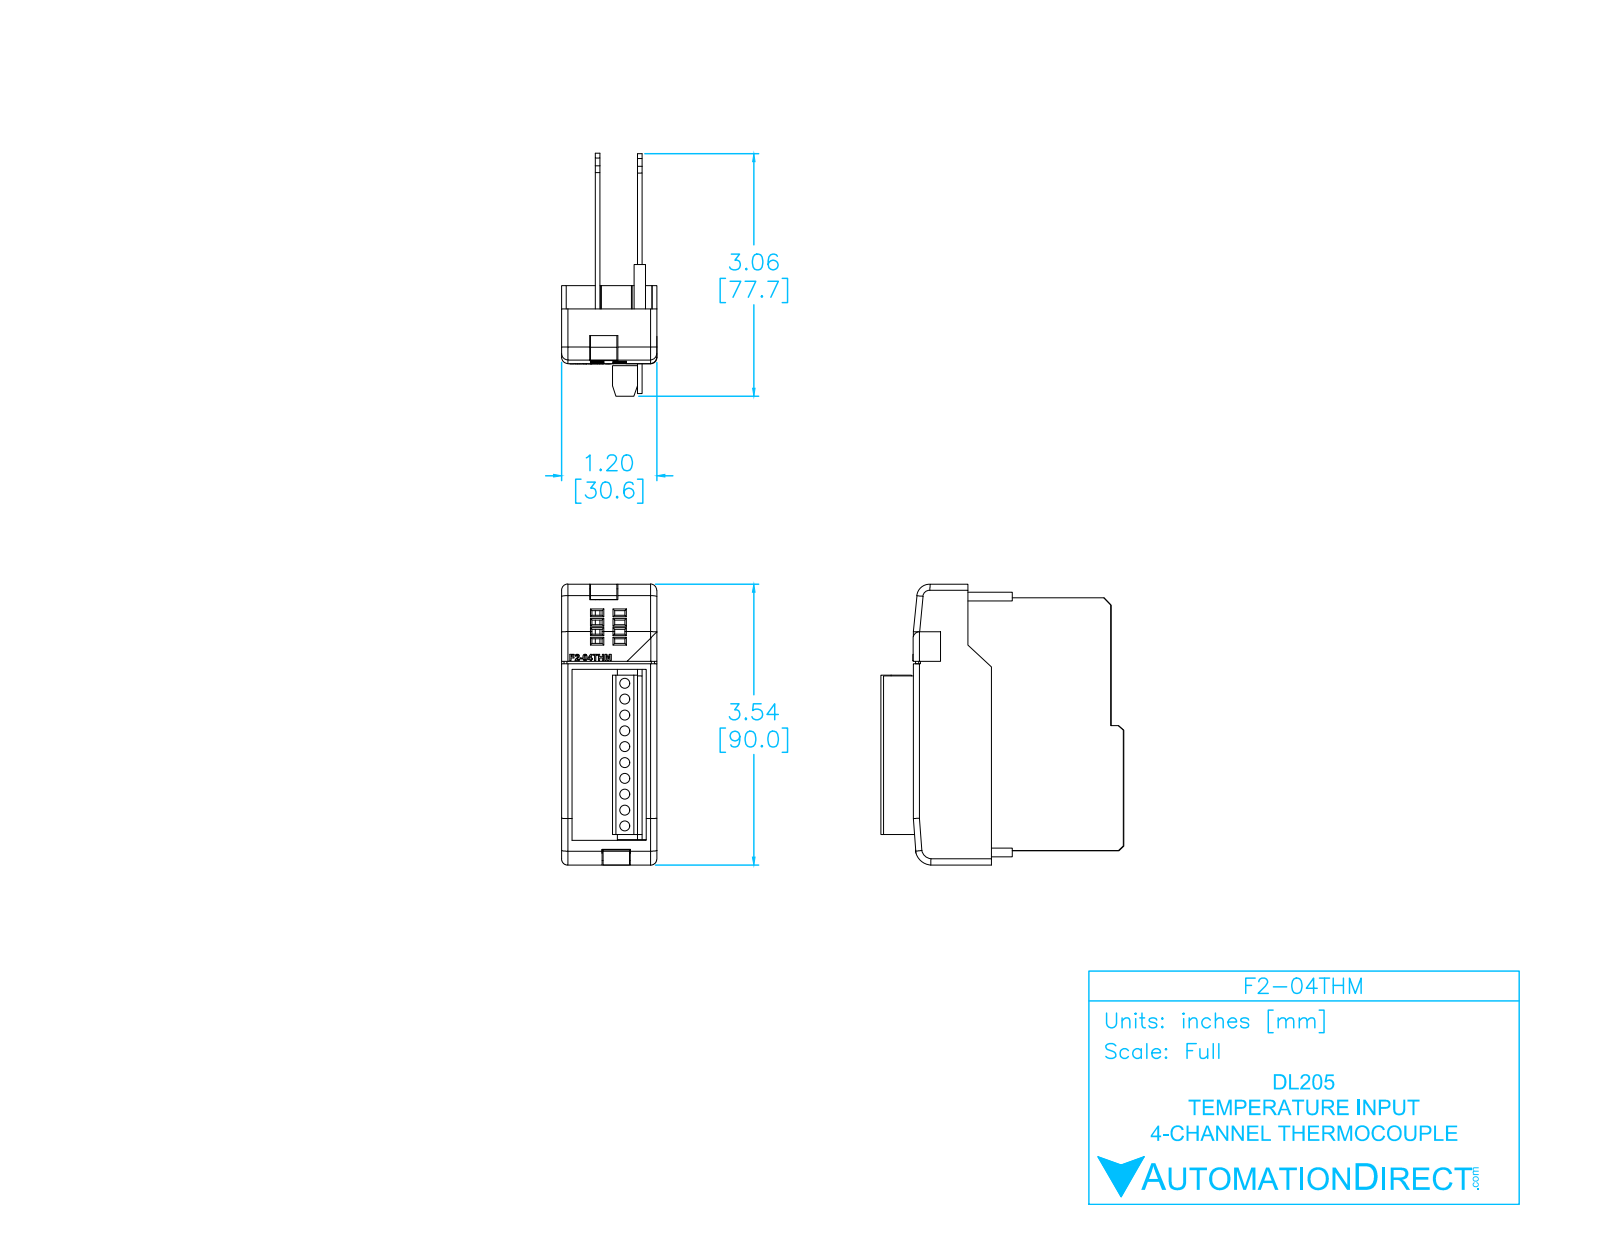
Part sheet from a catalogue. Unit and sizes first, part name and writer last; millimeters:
Units: millimetres
Overall size (bounding box): 90 × 77.81 × 30.55
Round holes (diameter × count): ⌀3.25 ×10
Partial cylindrical surfaces — rounded edges, fillets, slot ends (radius × count): R0.5 ×28, R2 ×11, R0.25 ×4, R1 ×2, R2.62 ×1, R3.79 ×1, R4.12 ×1, R5.29 ×1
Main face-to-face distances: 1.5, 13.5, 15, 12, 4.72, 18.22, 16.72, 3.22, 19.72, 6.22
Hole centre spacings: 10.15, 20.3, 5.07, 5.08, 15.22, 30.45, 15.23, 25.37
Volume: 27 664 mm³ · Surface area: 38 554 mm²
Bodies: 3 solids, 463 faces (333 planar, 104 cylindrical, 26 other)
Part name (STEP PRODUCT): F2-04THM
STEP written by: SolidWorks 2017 (AUTOMOTIVE_DESIGN)
